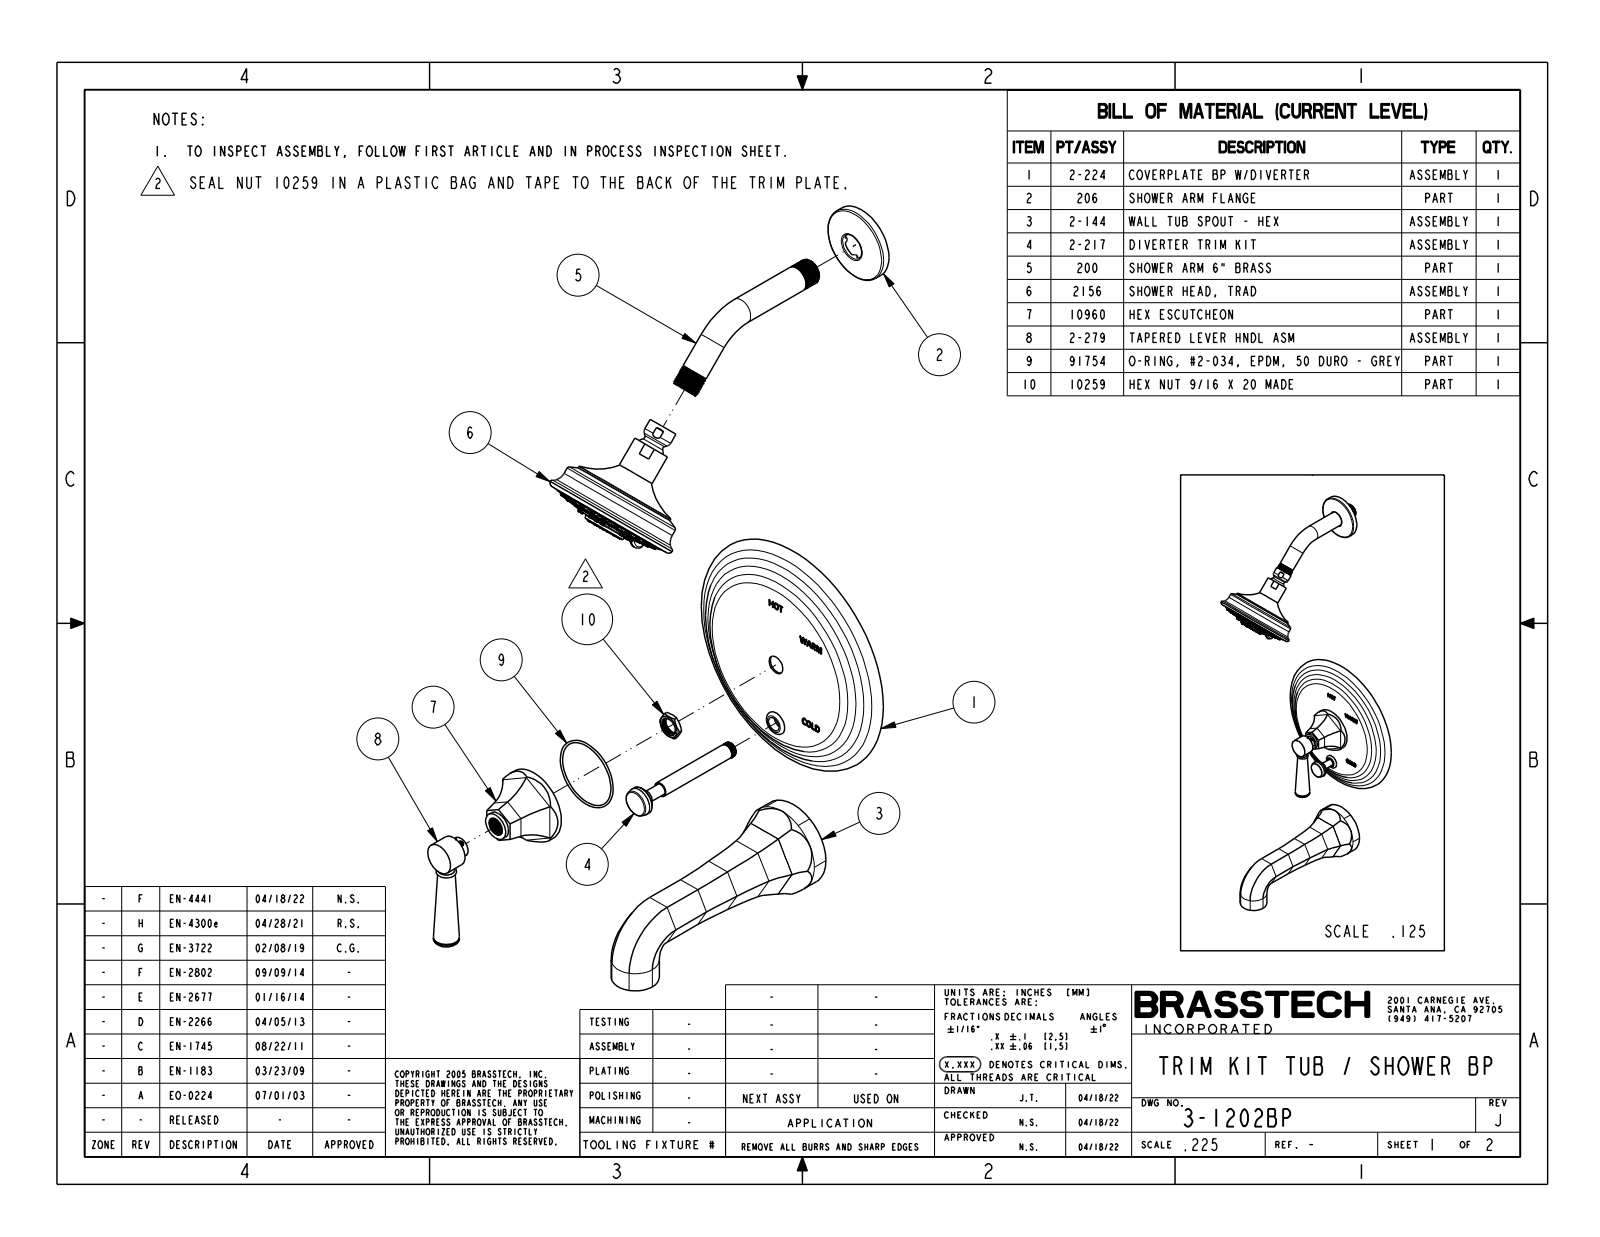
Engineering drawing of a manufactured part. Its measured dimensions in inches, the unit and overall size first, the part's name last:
Units: inches
Overall size (bounding box): 23.835 × 8.25 × 7.75
Round holes (diameter × count): ⌀0.059 ×8, ⌀0.385 ×1, ⌀0.925 ×1
Round bosses / shafts (diameter × count): ⌀0.142 ×39, ⌀0.165 ×23, ⌀0.813 ×2, ⌀3.81 ×1, ⌀3.724 ×1, ⌀3.24 ×1, ⌀2.8 ×1, ⌀2.38 ×1
Partial cylindrical surfaces — rounded edges, fillets, slot ends (radius × count): R0.079 ×8, R1.541 ×6, R2.125 ×6, R0.02 ×2, R0.138 ×1, R0.472 ×1, R0.512 ×1, R0.63 ×1
Main face-to-face distances: 0.754, 1.299, 0.995, 2.294, 0.063, 0.118, 0.181, 1.938, 1.184, 2.711
Hole centre spacings: 0.579, 0.443, 1.069, 0.818, 0.819, 1.157, 0.443, 1.069
Volume: 71.56 in³ · Surface area: 247.5 in²
Bodies: 3 solids, 1363 faces (258 planar, 230 cylindrical, 875 other)
Part name (STEP PRODUCT): 3-1202BP
STEP written by: CREO PARAMETRIC BY PTC INC, 2018400 (CONFIG_CONTROL_DESIGN)
